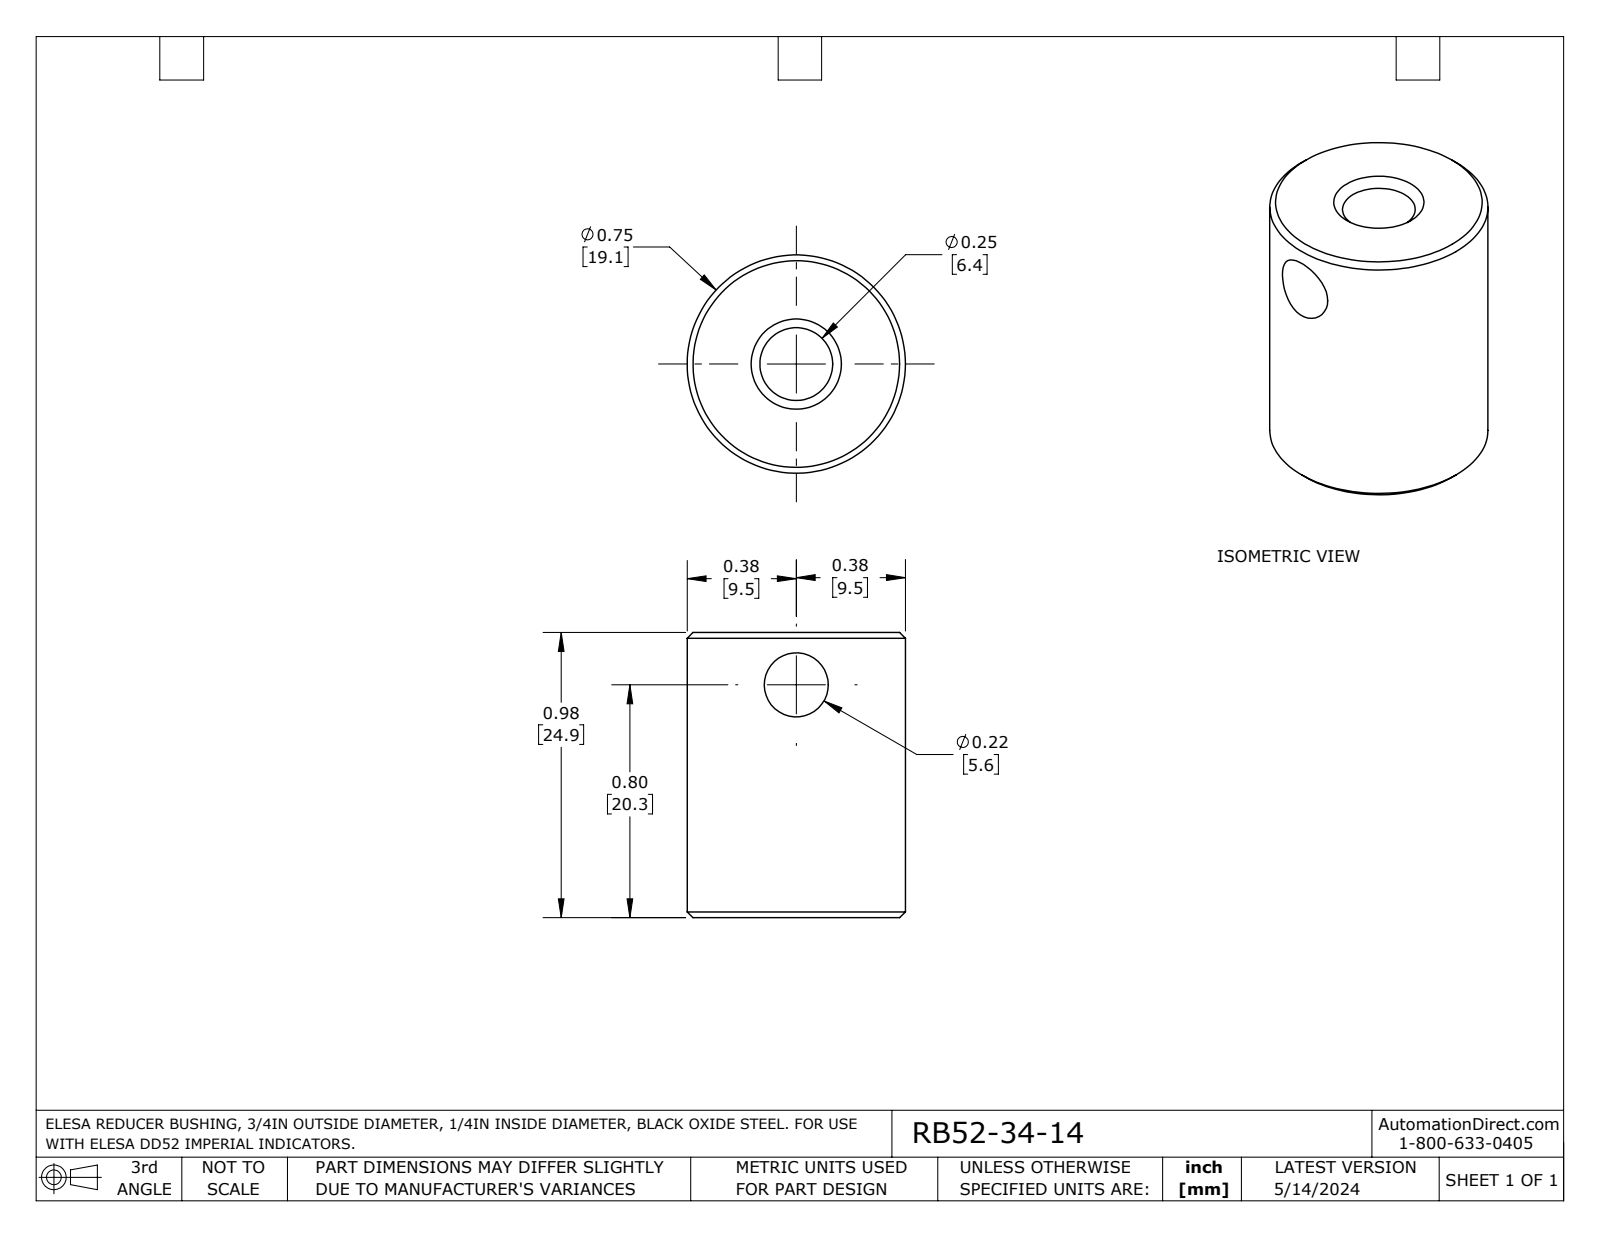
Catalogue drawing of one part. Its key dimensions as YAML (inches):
part_name: "RB52 3_4-1_4"
step_written_by: "SolidWorks 2023 (AUTOMOTIVE_DESIGN)"
units: inches
bodies: {solids: 1, faces: 9, planar: 2, cylindrical: 3, other: 4}
overall_size: [0.98, 0.75, 0.75]
volume: 0.373
surface_area: 3.888
round_holes:
  - {diameter: 0.22, count: 1}
  - {diameter: 0.25, count: 1}
round_bosses_or_shafts:
  - {diameter: 0.75, count: 1}
face_to_face_distances: [0.98]
